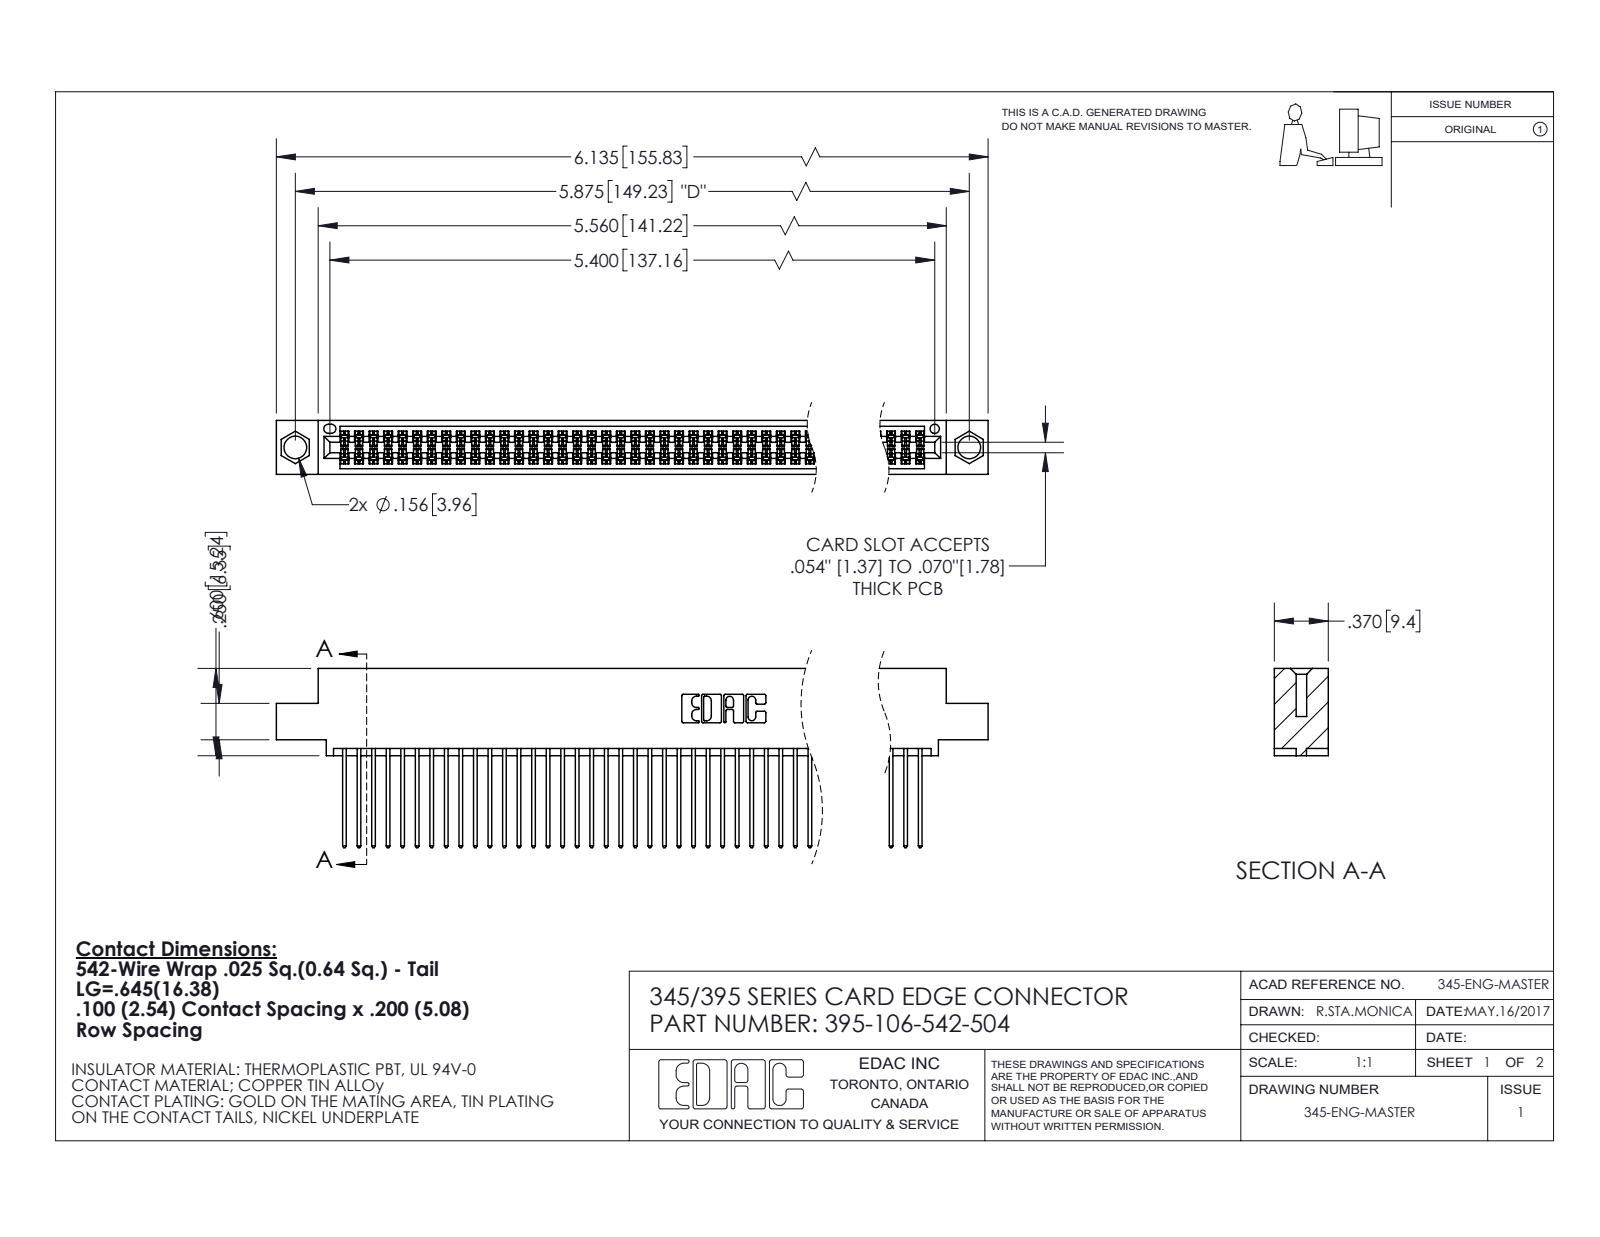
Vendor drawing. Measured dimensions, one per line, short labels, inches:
name: 345 Part_0.110 Offset - 0.156 Dia-TI; 395-106-542-504; 345-292-001_345-293-142
written by: SolidWorks 2020 (CONFIG_CONTROL_DESIGN)
unit: in
bodies: 107 solids, 5444 faces (3596 planar, 1848 cylindrical, 0 other)
size: 6.135 × 1.232 × 0.37
volume: 0.949 in³; area: 39.46 in²
holes: 2× ⌀0.156, 1× ⌀0.064
rounds: 159× R0.006, 106× R0.01, 22× R0.01, 6× R0.007, 6× R0.031, 3× R0.026, 2× R0.014, 2× R0.019
face distances: 0.298, 0.072, 0.2, 0.098, 0.272, 0.025, 0.225, 0.37, 0.175, 0.149
hole spacings: 0.27, 5.639, 5.875
